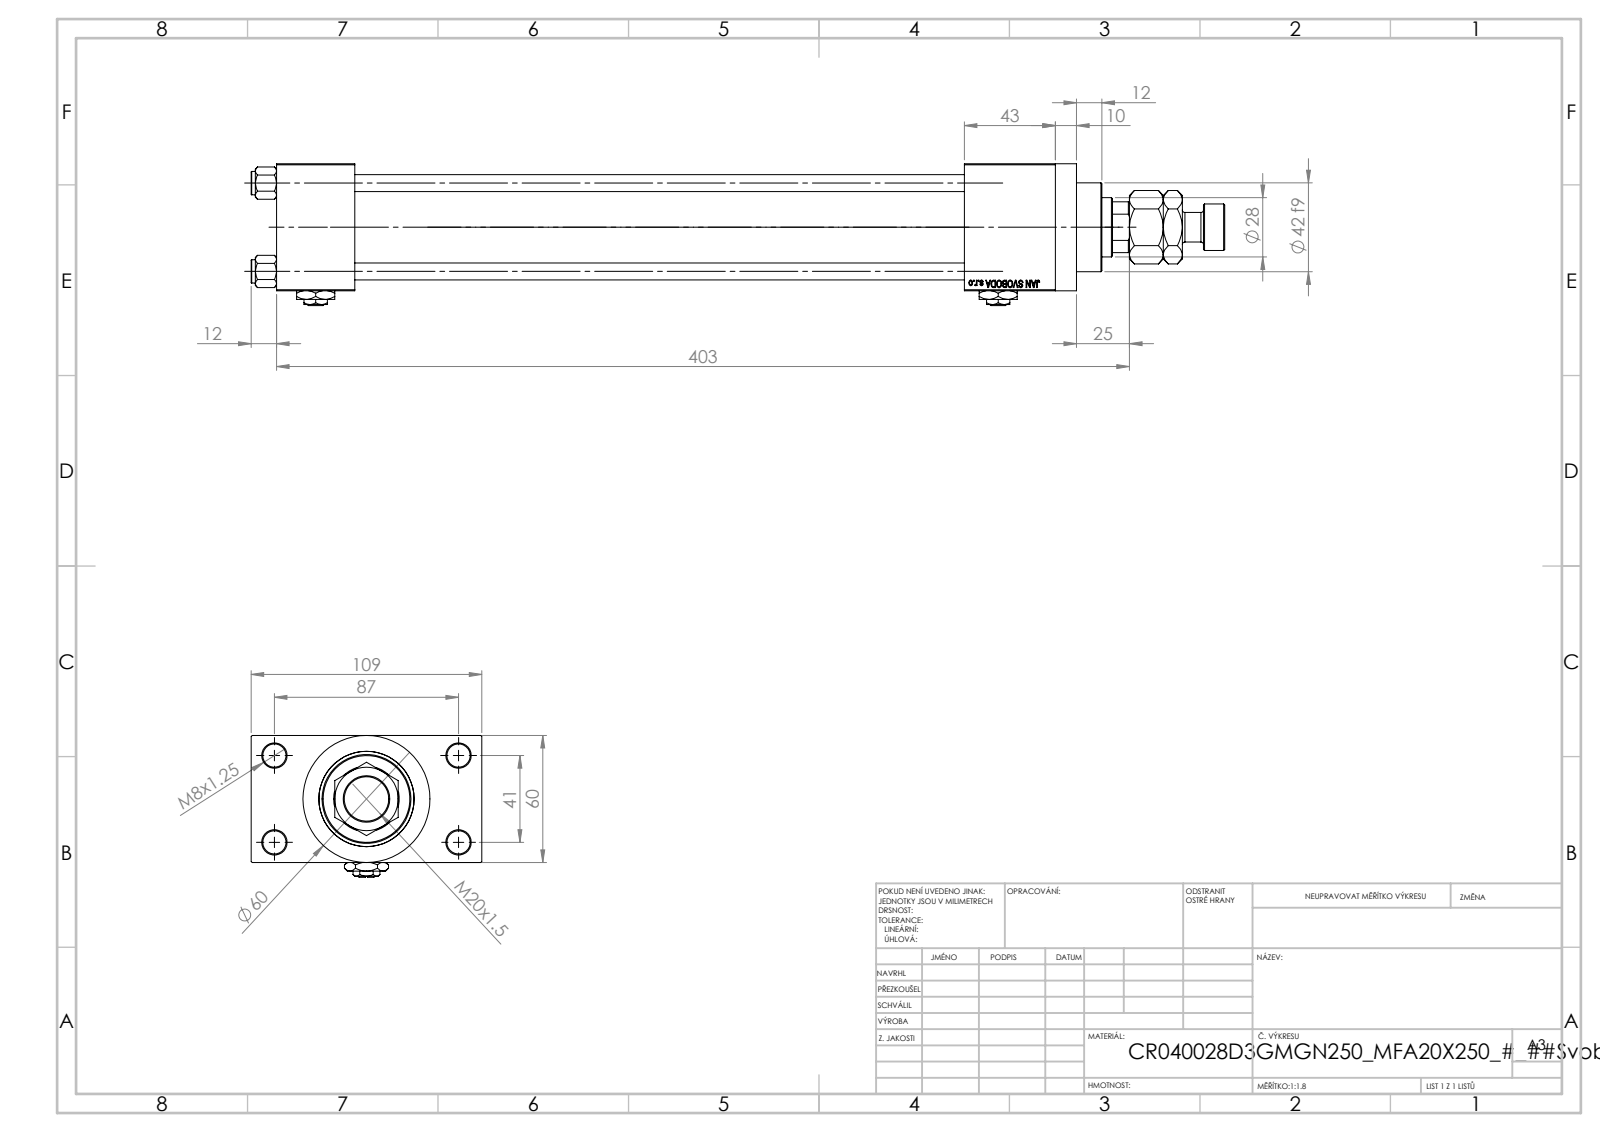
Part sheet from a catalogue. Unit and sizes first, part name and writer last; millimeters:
Units: millimetres
Overall size (bounding box): 460 × 109 × 67
Round holes (diameter × count): ⌀8 ×4, ⌀11 ×4, ⌀16.66 ×4, ⌀24 ×4, ⌀7 ×3, ⌀18.5 ×1, ⌀28 ×1, ⌀31 ×1, ⌀40 ×1, ⌀45 ×1
Round bosses / shafts (diameter × count): ⌀11 ×4, ⌀60 ×1, ⌀46 ×1, ⌀42 ×1, ⌀22 ×1, ⌀14 ×1
Partial cylindrical surfaces — rounded edges, fillets, slot ends (radius × count): R13.5 ×1
Main face-to-face distances: 60, 24.5, 288, 84.5, 37, 325, 43, 368, 331, 109
Hole centre spacings: 22.65, 29.49, 41.7, 47.15, 48.09, 64.35, 76.49, 41
Volume: 832 727 mm³ · Surface area: 242 748 mm²
Bodies: 14 solids, 1257 faces (562 planar, 103 cylindrical, 592 other)
Part name (STEP PRODUCT): Zatka_pro_OIL_PORT; MFA; V215CR_D_Body; NUT_M5_D (+3 more)
STEP written by: SolidWorks 2019 (CONFIG_CONTROL_DESIGN)
